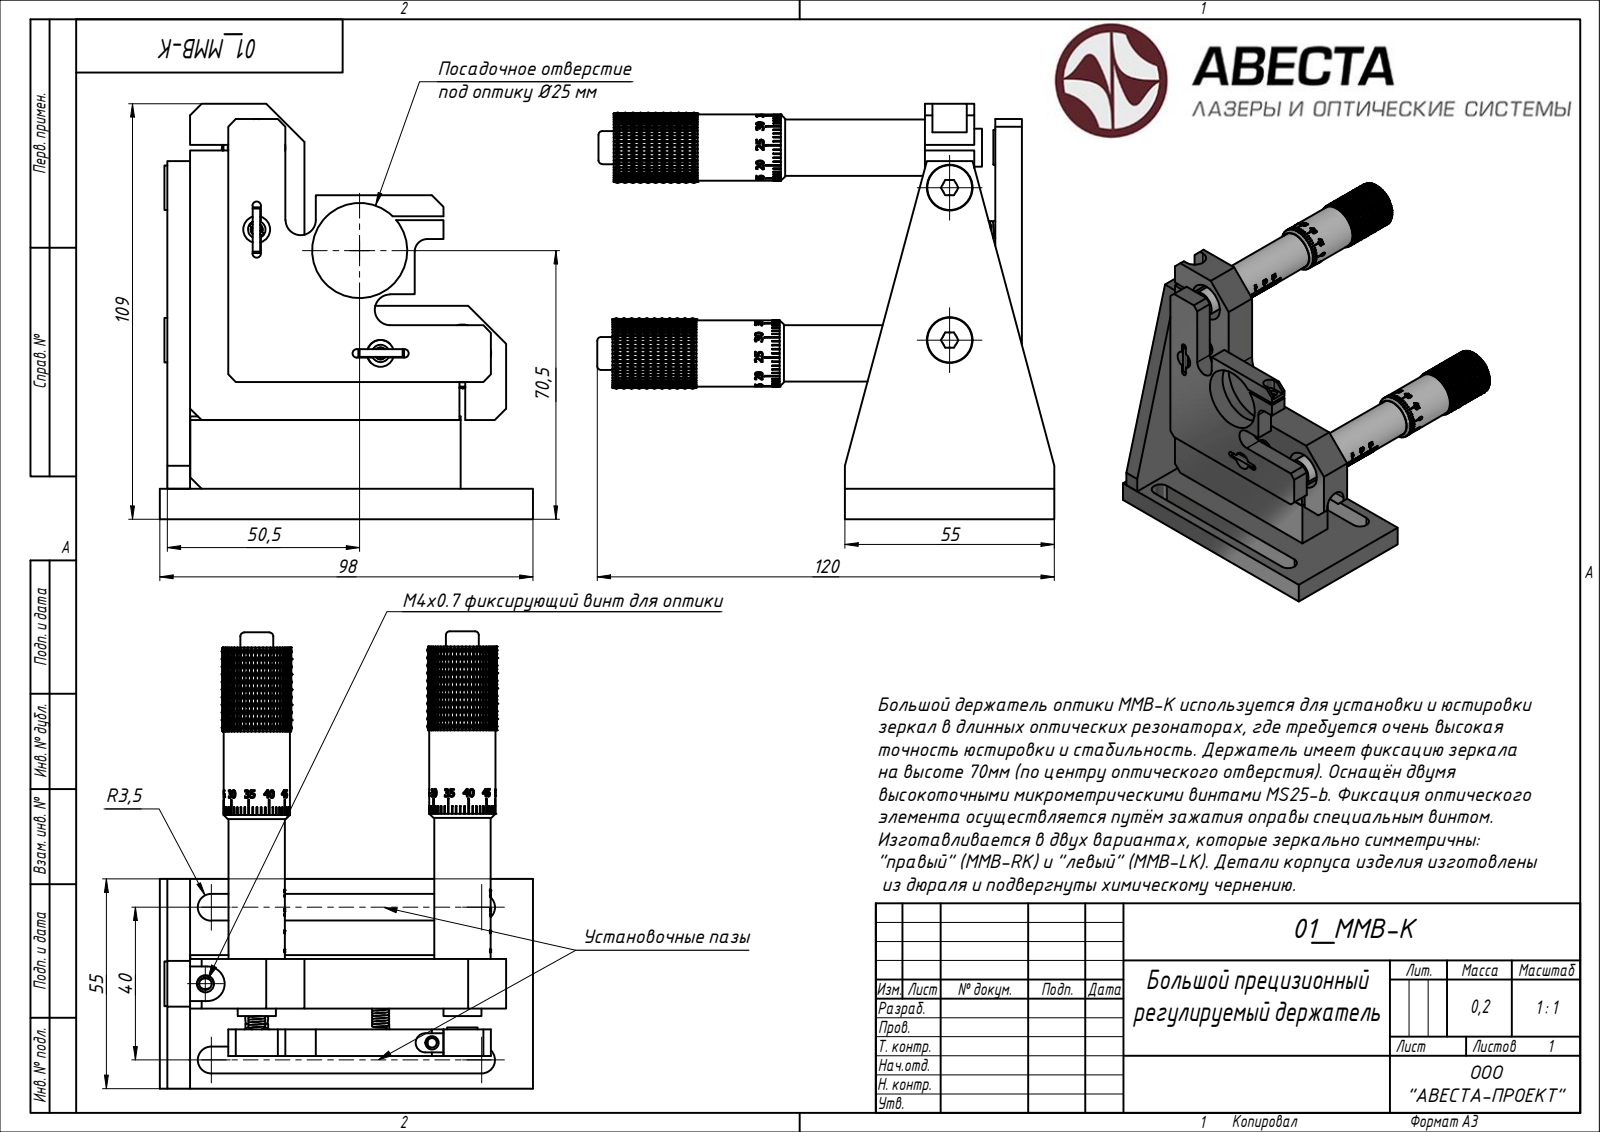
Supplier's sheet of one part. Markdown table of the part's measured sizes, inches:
| quantity | value |
| --- | --- |
| STEP written by | ST-DEVELOPER v15 (AUTOMOTIVE_DESIGN) |
| units | inches |
| bodies | 21 solids, 393 faces (145 planar, 0 cylindrical, 248 other) |
| overall size | 4.291 × 4.268 × 3.858 |
| volume | 10.05 in³ |
| surface area | 95.59 in² |
| main face-to-face distances | 0.315, 0.512, 0.276, 0.236, 1.003, 0.491, 0.728, 0.216, 1.024, 0.709 |
